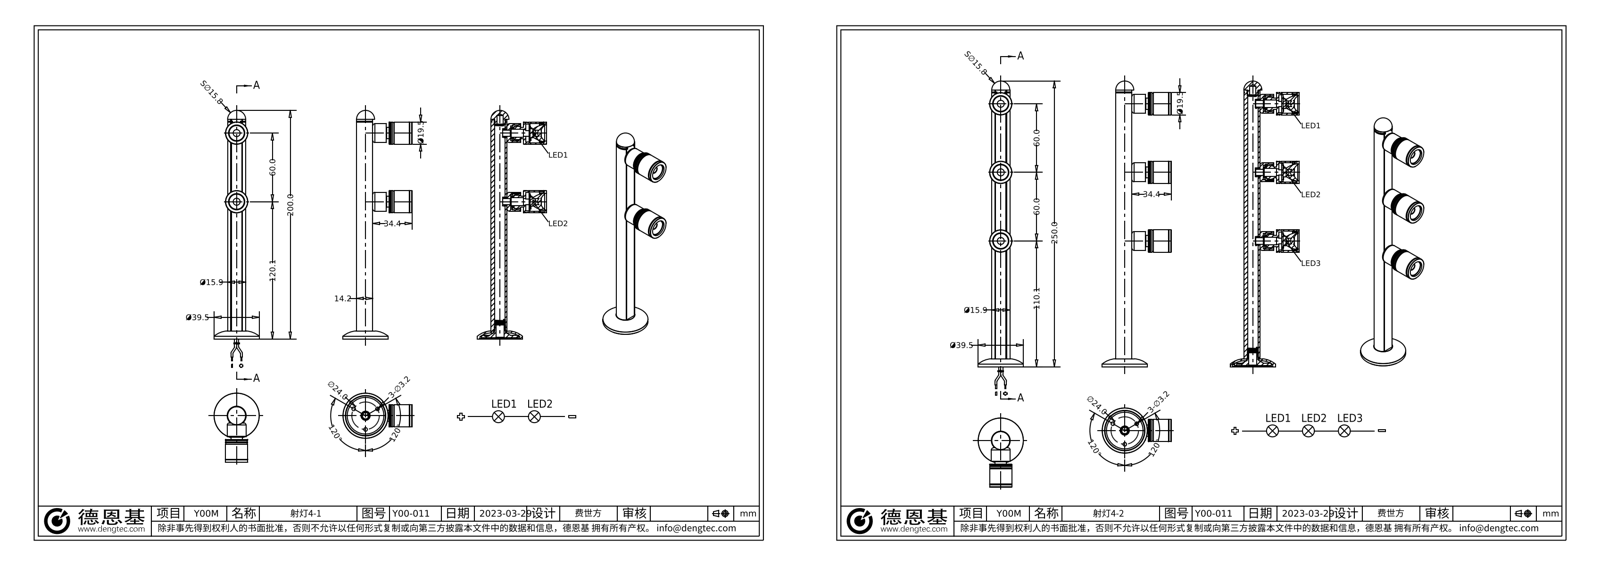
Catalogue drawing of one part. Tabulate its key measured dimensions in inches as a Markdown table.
| quantity | value |
| --- | --- |
| part name | 固定座; 橡胶圈; 灯板; 底座上盖 (+8 more) |
| STEP written by | SolidWorks 2018 (CONFIG_CONTROL_DESIGN) |
| units | inches |
| bodies | 24 solids, 650 faces (222 planar, 257 cylindrical, 171 other) |
| overall size | 7.874 × 2.38 × 1.555 |
| volume | 2.442 in³ |
| surface area | 57.22 in² |
| round holes (diameter × count) | 0.272 × 5, 0.236 × 4, 0.126 × 3, 0.217 × 3, 0.205 × 2, 0.228 × 2, 0.241 × 2, 0.268 × 2, 0.311 × 2, 0.457 × 2, 0.508 × 2, 0.559 × 2 |
| round bosses / shafts (diameter × count) | 0.768 × 2, 0.728 × 2, 0.65 × 2, 0.551 × 2, 0.541 × 2, 0.383 × 2, 0.315 × 2, 0.276 × 2 |
| partial cylindrical surfaces (radius × count) | 0.039 × 10, 0.012 × 8, 0.004 × 4, 0.02 × 4, 0.315 × 2, 0.313 × 1 |
| main face-to-face distances | 0.75, 0.797, 0.047, 0.569, 0.181, 0.228, 0.091, 0.606, 0.083, 0.098 |
| hole center spacings | 0.818, 0.196, 0.197, 0.472, 0.393, 0.394, 0.472, 1.971 |
